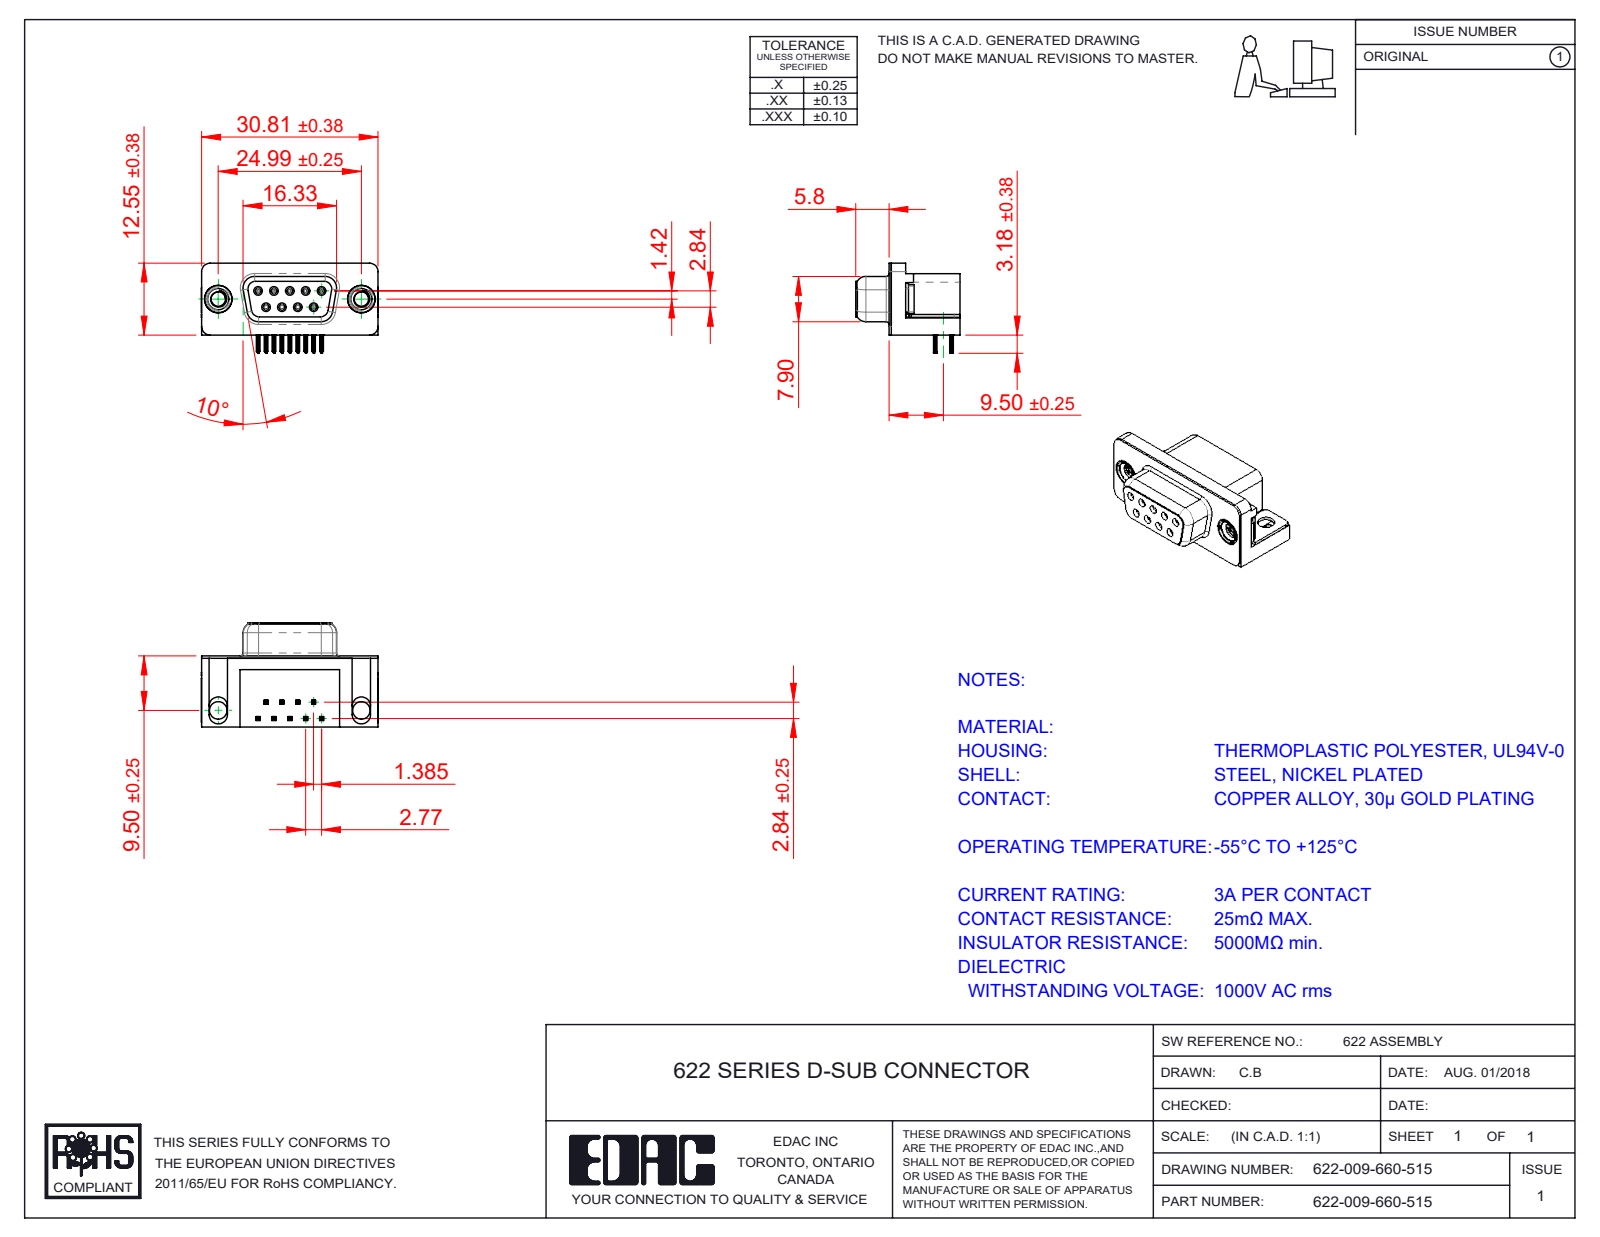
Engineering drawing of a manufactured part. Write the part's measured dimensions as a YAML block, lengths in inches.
part_name: "622 Contact Top; 622 Socket Bottom; 622 M3 Threaded Rivet; 622 Shell_9 Socket (+3 more)"
step_written_by: "SolidWorks 2016 (CONFIG_CONTROL_DESIGN)"
units: inches
bodies: {solids: 15, faces: 1570, planar: 682, cylindrical: 420, other: 468}
overall_size: [1.216, 0.717, 0.619]
volume: 0.227
surface_area: 7.849
round_holes:
  - {diameter: 0.031, count: 9}
  - {diameter: 0.035, count: 9}
  - {diameter: 0.098, count: 2}
  - {diameter: 0.12, count: 2}
  - {diameter: 0.157, count: 2}
  - {diameter: 0.189, count: 2}
  - {diameter: 0.197, count: 2}
round_bosses_or_shafts:
  - {diameter: 0.047, count: 9}
  - {diameter: 0.193, count: 2}
  - {diameter: 0.187, count: 2}
  - {diameter: 0.154, count: 2}
partial_cylinders:
  - {radius: 0.004, count: 72}
  - {radius: 0.006, count: 36}
  - {radius: 0.014, count: 18}
  - {radius: 0.039, count: 18}
  - {radius: 0.013, count: 9}
  - {radius: 0.01, count: 8}
  - {radius: 0.053, count: 8}
  - {radius: 0.063, count: 8}
face_to_face_distances: [0.016, 0.472, 0.488, 0.014, 0.114, 0.098, 0.244, 0.407, 0.02, 0.374]
hole_center_spacings: [0.124, 0.109, 0.218, 0.198, 0.198, 0.327, 0.294, 0.295]
